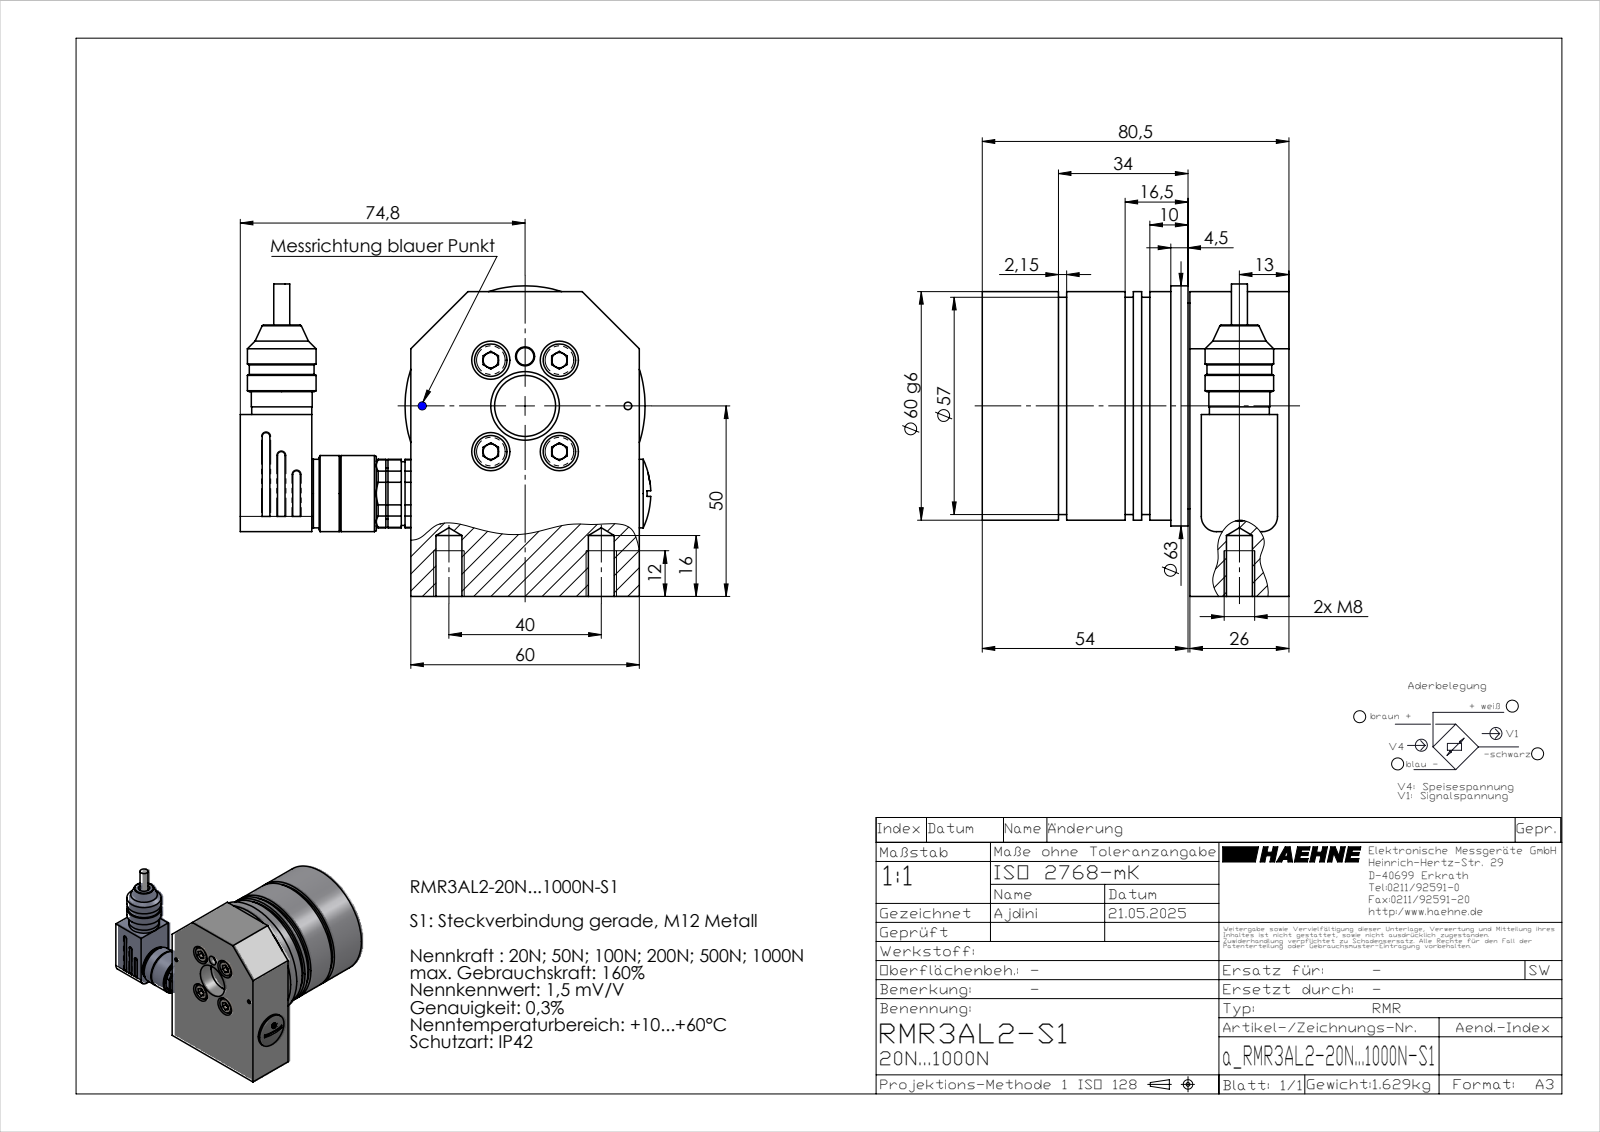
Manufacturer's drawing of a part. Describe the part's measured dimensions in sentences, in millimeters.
The part is named "a_RMR3AL2-20N...1000N-S1". Its 3-D file was written by "SolidWorks 2023 (AUTOMOTIVE_DESIGN)". It is 17 solids with 556 faces: 279 planar, 181 cylindrical and 96 other. Overall it measures 107.74 by 81.98 by 80.5 millimeters. Its volume is 250 609 cubic millimeters and its surface area 77 185 square millimeters. Round holes: 4 of diameter 4.2, 4 of diameter 5.3, 4 of diameter 10, 2 of diameter 2, 2 of diameter 6.8, 1 of diameter 0.64, 1 of diameter 3, 1 of diameter 4.5, 1 of diameter 5, 1 of diameter 6, 1 of diameter 8.37, 1 of diameter 11.5. Round bosses or shafts: 5 of diameter 0.86, 4 of diameter 8.5, 4 of diameter 5, 4 of diameter 1.5, 4 of diameter 1, 2 of diameter 18, 2 of diameter 16, 1 of diameter 63. Partial cylindrical surfaces (rounded edges, fillets, slot ends): 12 of radius 0.2, 11 of radius 1, 6 of radius 0.3, 2 of radius 4, 1 of radius 0.57, 1 of radius 0.65, 1 of radius 0.77, 1 of radius 3.5. The main face-to-face distances are 11.5, 48.5, 37, 26, 73, 54.5, 15, 11, 62, 47. The hole center spacings are 15, 21.63, 37.95, 9.06, 18, 24, 26.57, 27.
